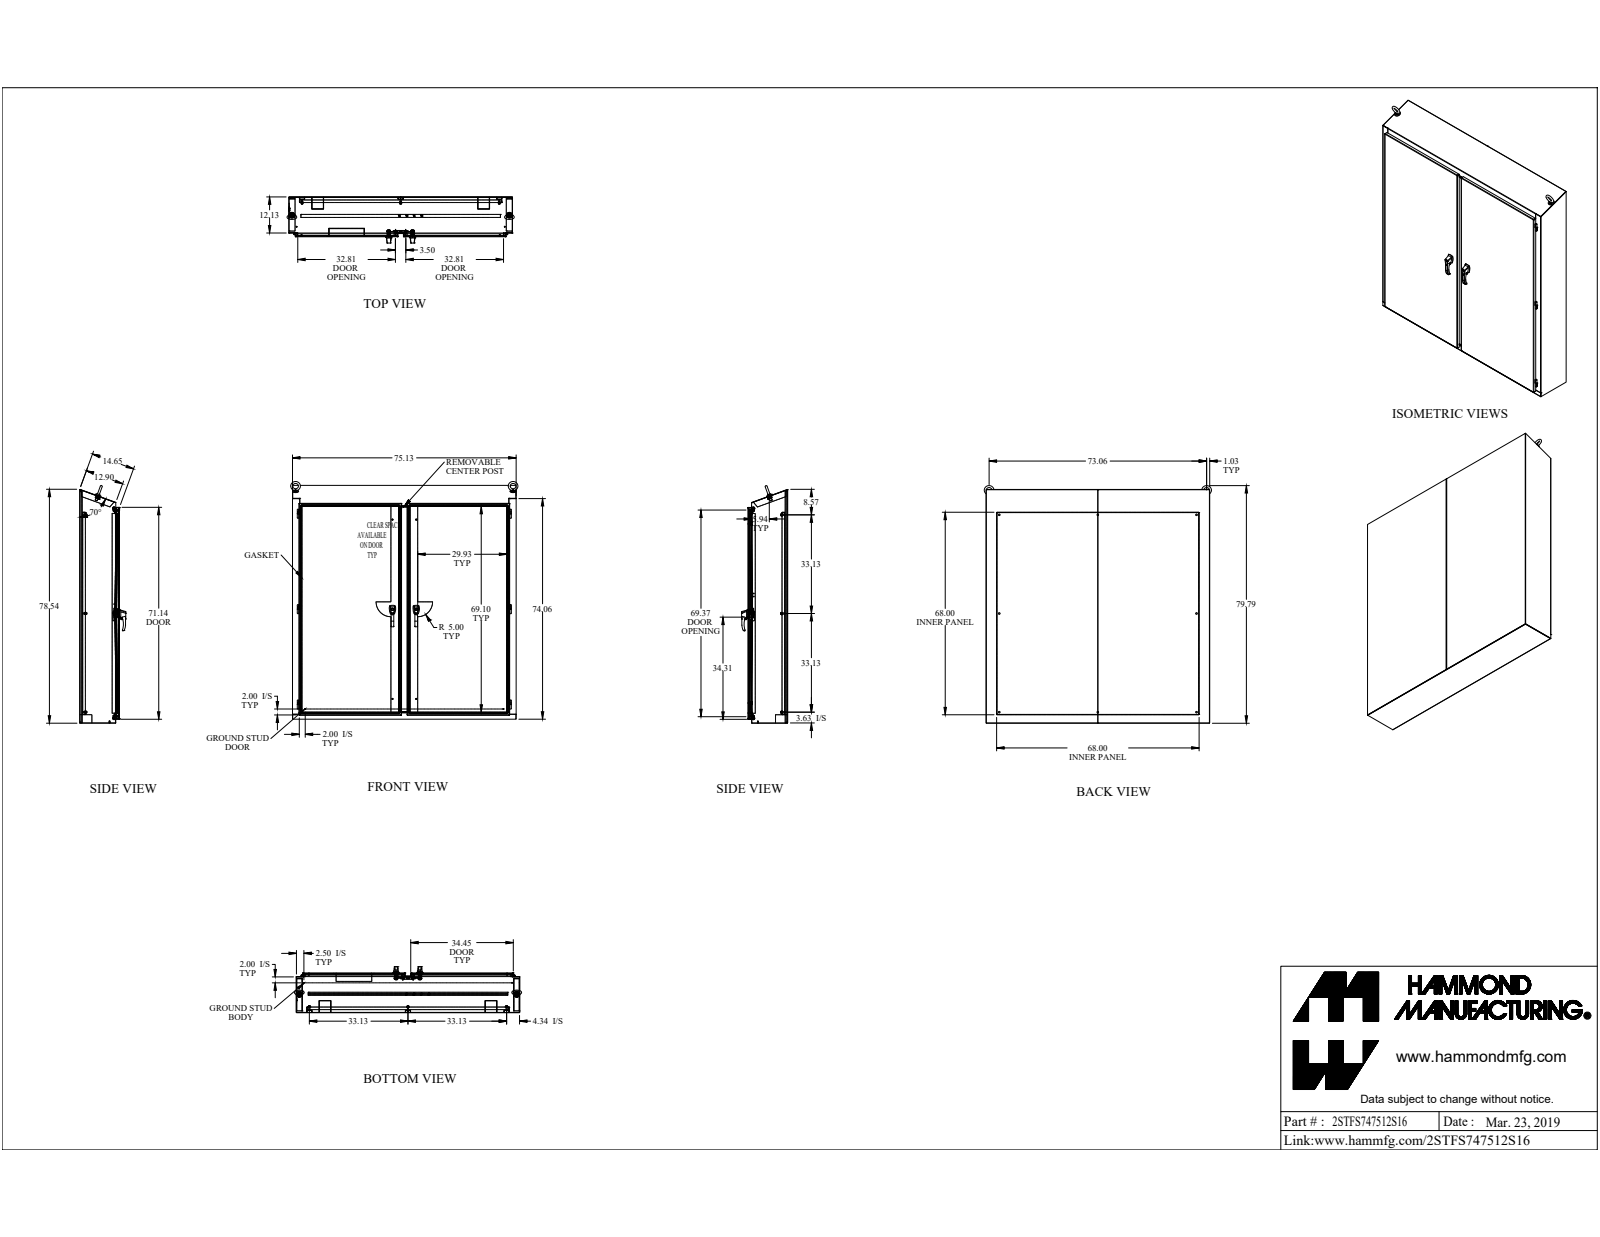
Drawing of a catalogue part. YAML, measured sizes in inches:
part_name: "2STFS747512S16"
step_written_by: "SolidWorks 2019 (CONFIG_CONTROL_DESIGN)"
units: inches
bodies: {solids: 146, faces: 2404, planar: 1417, cylindrical: 729, other: 258}
overall_size: [79.792, 76.307, 15.491]
volume: 2414
surface_area: 47837
round_holes:
  - {diameter: 0.307, count: 8}
  - {diameter: 0.35, count: 8}
  - {diameter: 0.563, count: 8}
  - {diameter: 0.25, count: 7}
  - {diameter: 0.281, count: 6}
  - {diameter: 0.313, count: 6}
  - {diameter: 0.445, count: 6}
  - {diameter: 0.196, count: 4}
  - {diameter: 0.257, count: 4}
  - {diameter: 0.28, count: 4}
  - {diameter: 0.39, count: 4}
  - {diameter: 0.413, count: 4}
round_bosses_or_shafts:
  - {diameter: 1, count: 12}
  - {diameter: 0.65, count: 8}
  - {diameter: 0.375, count: 8}
  - {diameter: 0.332, count: 8}
  - {diameter: 0.75, count: 4}
  - {diameter: 0.63, count: 4}
  - {diameter: 0.625, count: 4}
  - {diameter: 0.44, count: 4}
partial_cylinders:
  - {radius: 0.125, count: 47}
  - {radius: 0.5, count: 33}
  - {radius: 0.018, count: 32}
  - {radius: 0.048, count: 30}
  - {radius: 0.143, count: 30}
  - {radius: 0.06, count: 20}
  - {radius: 0.25, count: 16}
  - {radius: 0.03, count: 12}
face_to_face_distances: [0.095, 0.095, 13.185, 13.28, 13.281, 13.376, 0.125, 11.469, 11.373, 1.812]
hole_center_spacings: [73.059, 7.983, 74.07, 66.25, 7.443, 29.544, 30.098, 30.104]
